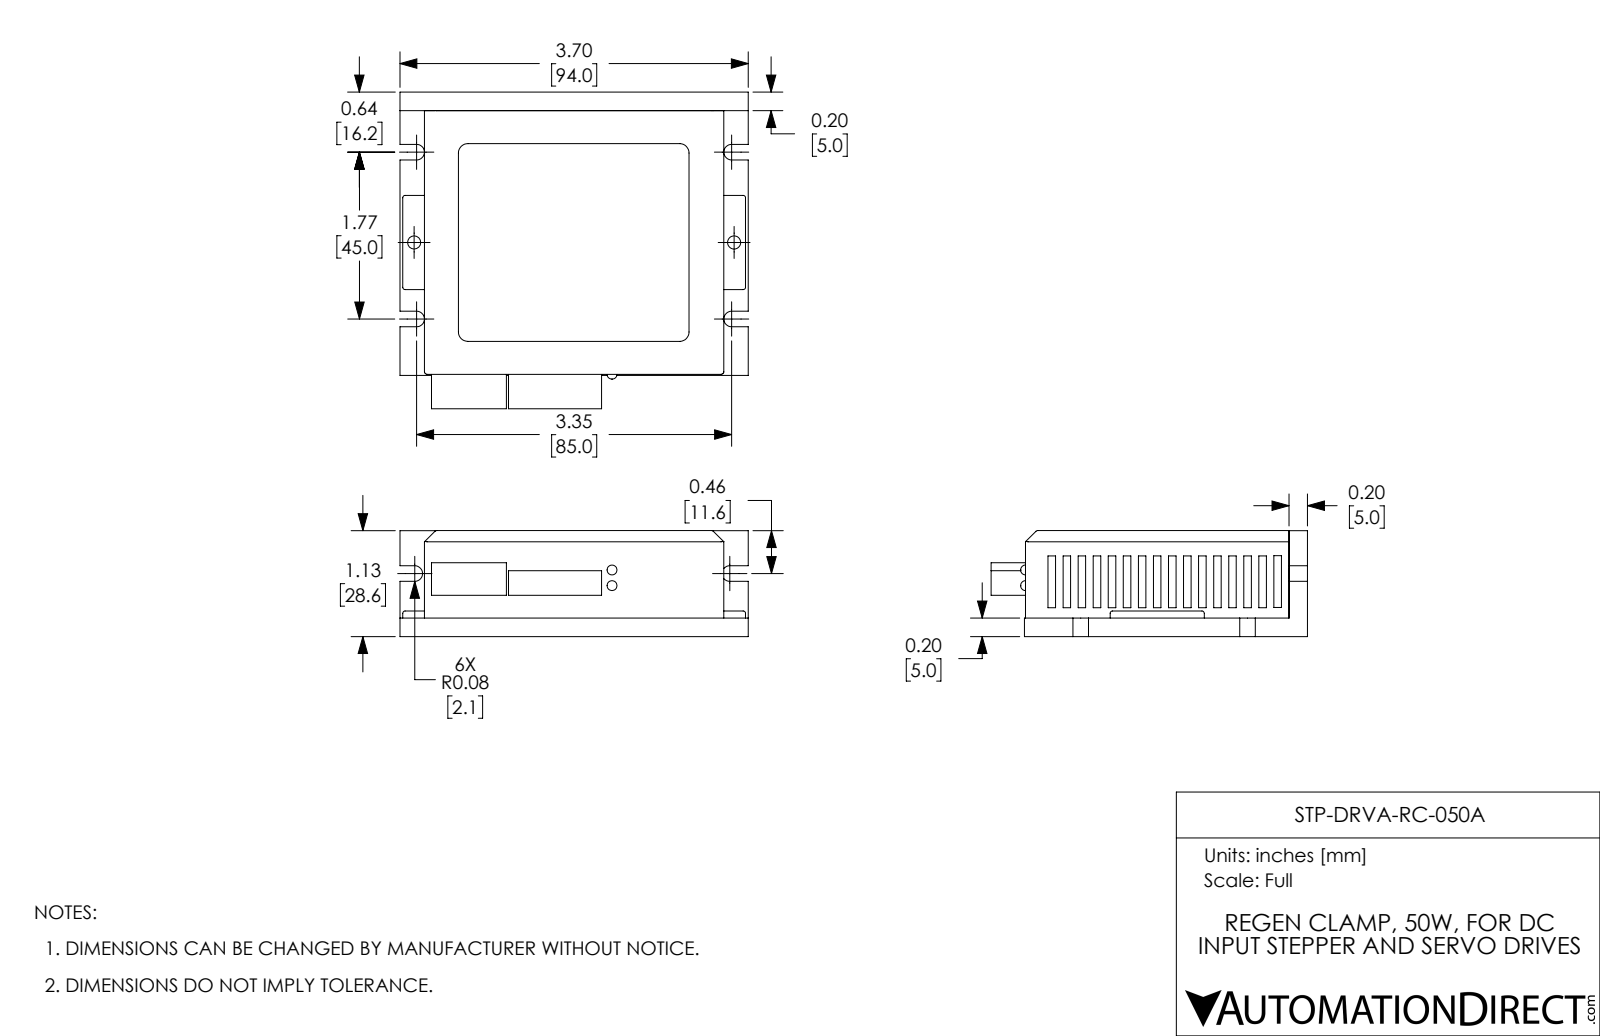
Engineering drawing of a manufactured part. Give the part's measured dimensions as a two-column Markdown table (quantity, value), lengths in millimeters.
| quantity | value |
| --- | --- |
| part name | RC880 |
| STEP written by | SolidWorks 2017 (AUTOMOTIVE_DESIGN) |
| units | millimeters |
| bodies | 1 solid, 251 faces (206 planar, 35 cylindrical, 10 other) |
| overall size | 94 × 85.4 × 28.6 |
| volume | 65 730 mm³ |
| surface area | 42 070 mm² |
| round holes (diameter × count) | 3.6 × 2 |
| partial cylindrical surfaces (radius × count) | 0.6 × 9, 0.8 × 7, 2.1 × 6, 2.5 × 4 |
| main face-to-face distances | 5, 21.7, 26.7, 28.2, 23.2, 1.5, 1.9, 28.6, 23.6, 0.4 |
| hole center spacings | 86.4 |
